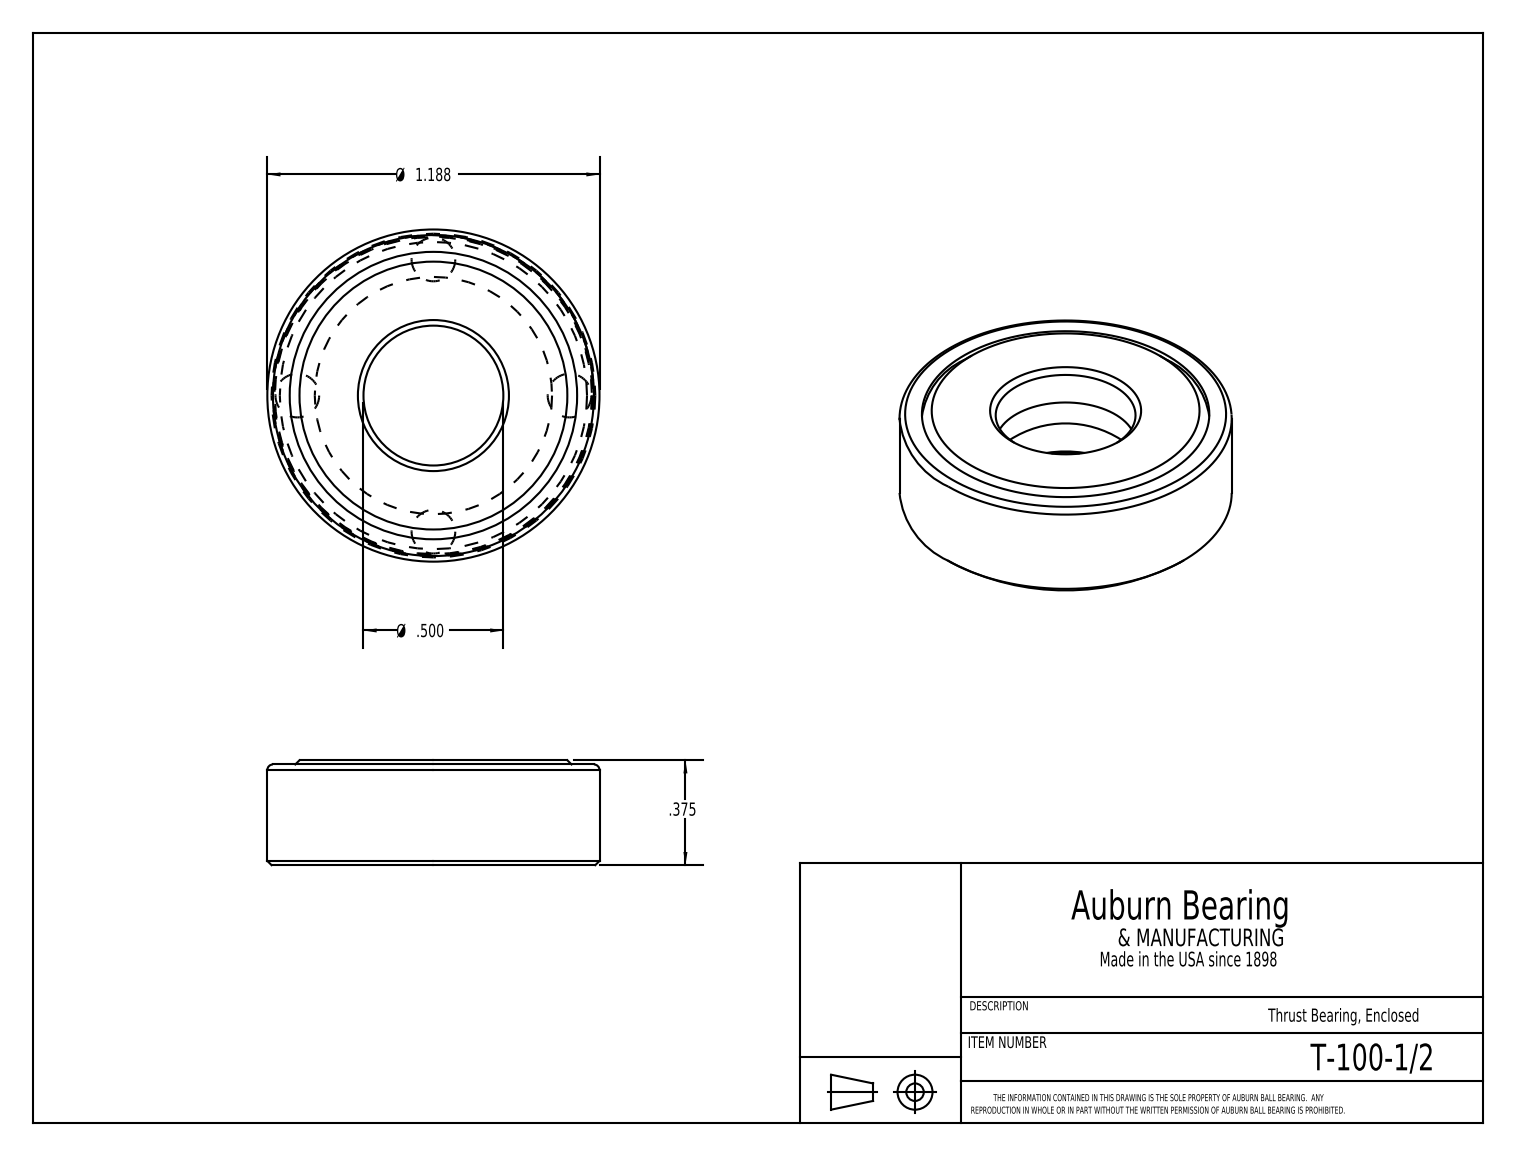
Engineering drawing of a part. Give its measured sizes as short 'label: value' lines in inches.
name: T-100-1-2
written by: SolidWorks 2016 (CONFIG_CONTROL_DESIGN)
unit: in
bodies: 6 solids, 28 faces (9 planar, 7 cylindrical, 12 other)
size: 1.188 × 1.188 × 0.375
volume: 0.239 in³; area: 7.086 in²
holes: 1× ⌀0.5, 1× ⌀1.027, 1× ⌀1.147
bosses: 1× ⌀1.187, 1× ⌀1.133
face distances: 0.375, 0.141, 0.235, 0.234, 0.094, 0.141, 0.34, 0.2, 0.106, 0.035
